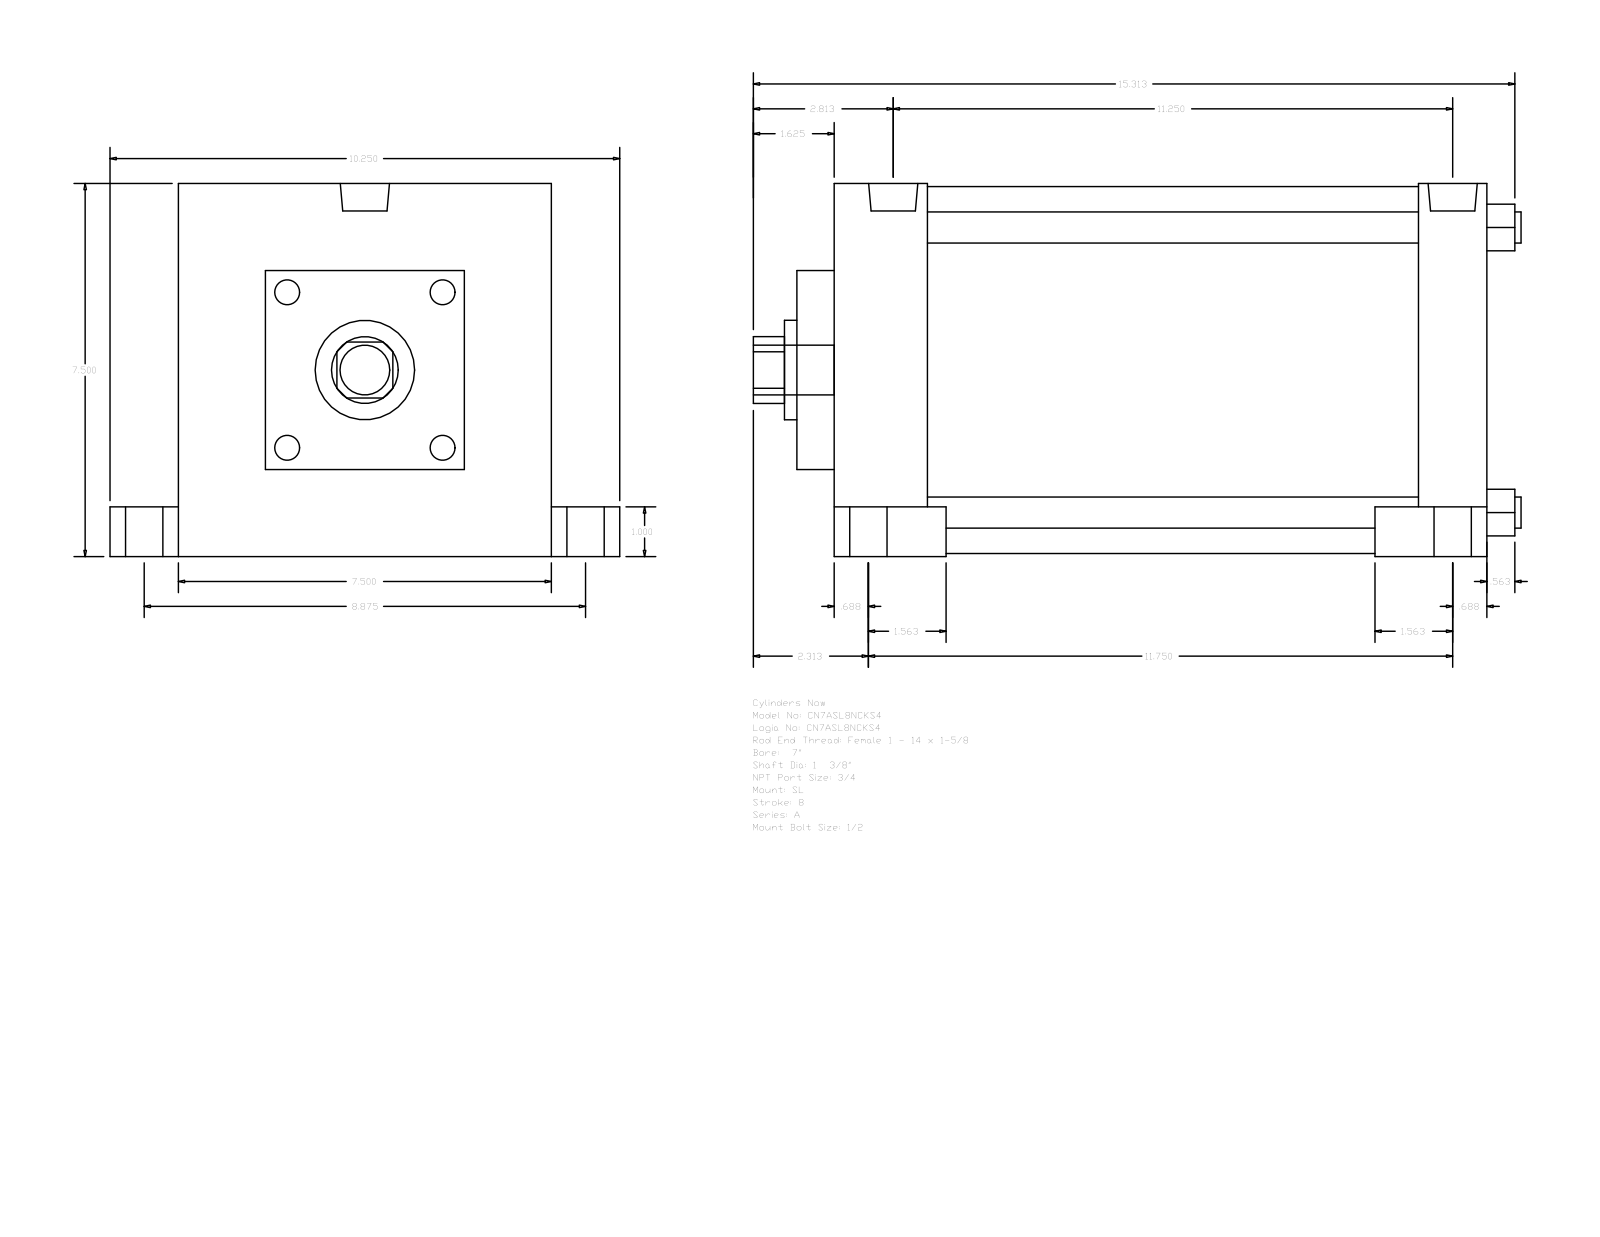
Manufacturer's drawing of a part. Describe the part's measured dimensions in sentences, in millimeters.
The part is named "A_SL__0700_1.375". Its 3-D file was written by "GSSL Pune (CONFIG_CONTROL_DESIGN)". It is 0 solids with 117 faces: 85 planar, 32 cylindrical and 0 other. Overall it measures 392.11 by 260.35 by 190.5 millimeters. Round holes: 4 of diameter 15.88, 1 of diameter 34.92, 1 of diameter 50.8, 1 of diameter 187.32. Round bosses or shafts: 5 of diameter 25.4, 4 of diameter 19.05, 4 of diameter 15.08, 2 of diameter 25.12. Partial cylindrical surfaces (rounded edges, fillets, slot ends): 1 of radius 17.06. The main face-to-face distances are 190.5, 333.38, 19.04, 352.42, 317.5, 66.67, 47.63, 285.75, 298.46, 250.83. The hole center spacings are 102.91, 145.54, 205.82.
